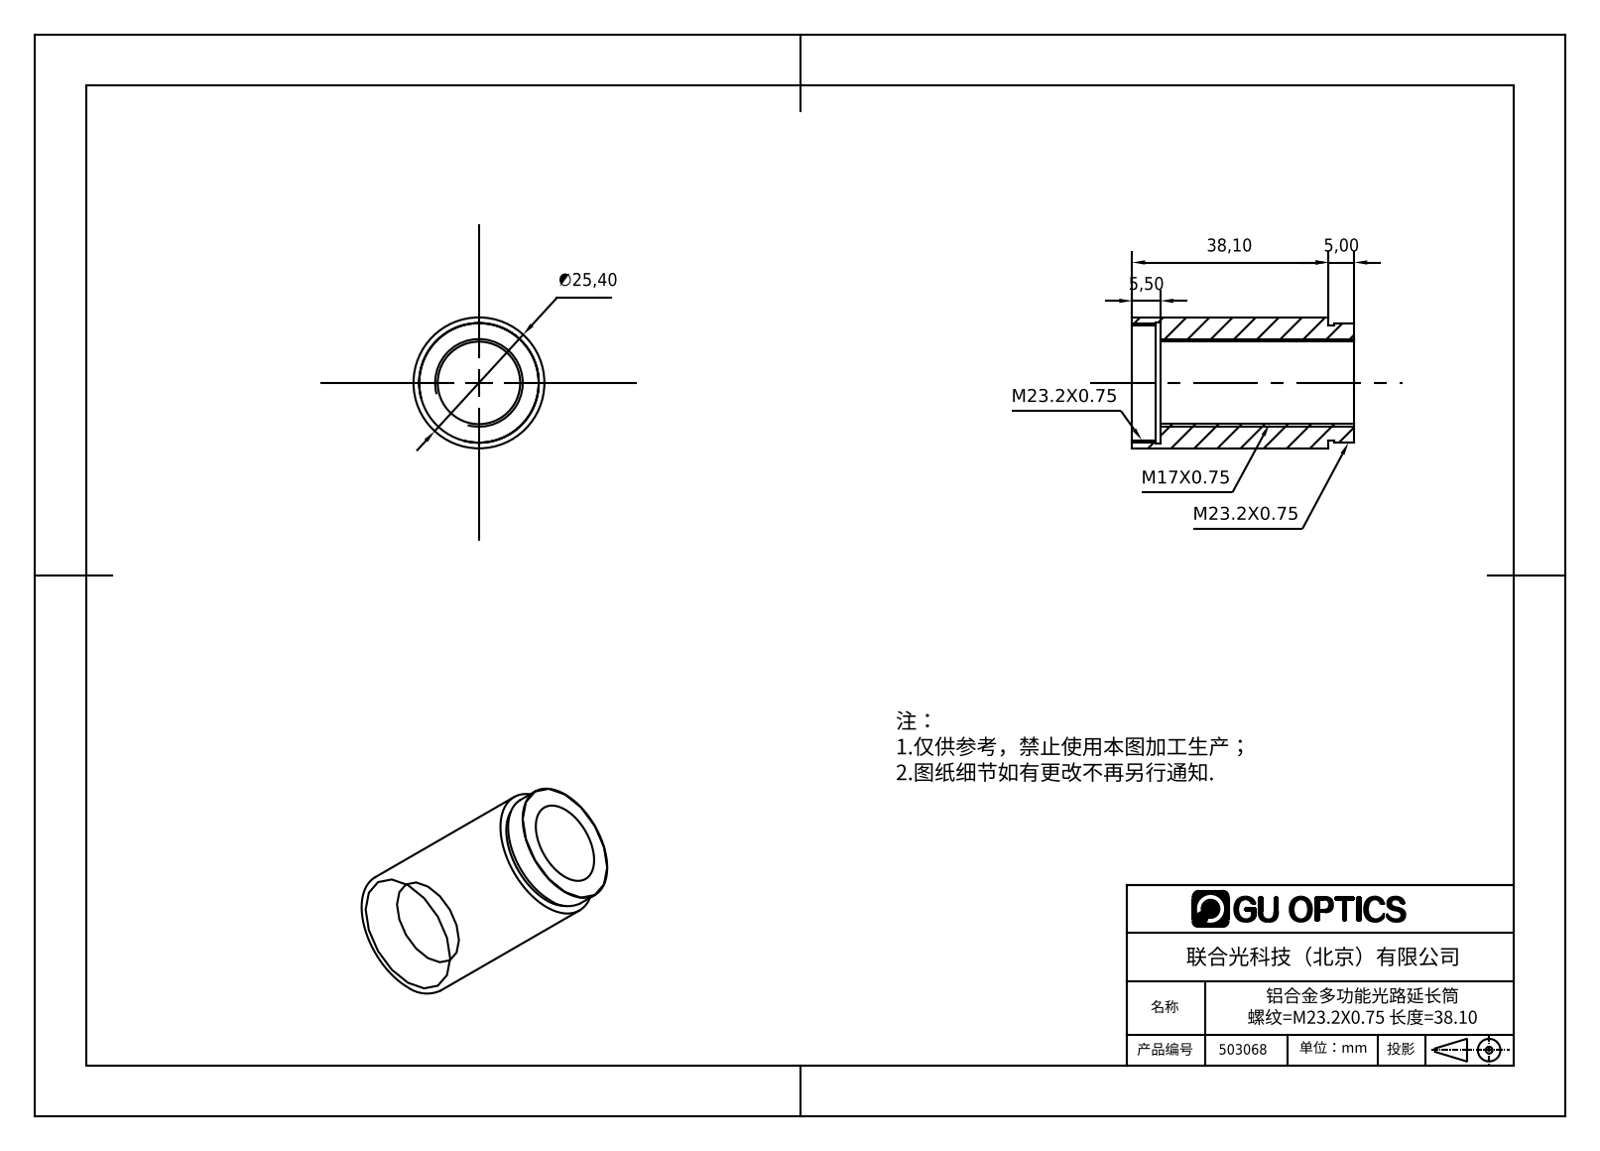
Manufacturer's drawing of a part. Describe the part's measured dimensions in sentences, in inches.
The part is named "503068". Its 3-D file was written by "SolidWorks 2016 (AUTOMOTIVE_DESIGN)". It is 1 solid with 18 faces: 6 planar, 12 cylindrical and 0 other. Overall it measures 1.697 by 1 by 1 inches. Its volume is 0.711 cubic inches and its surface area 9.993 square inches. Round holes: 1 of diameter 0.63, 1 of diameter 0.874, 1 of diameter 0.921. Round bosses or shafts: 1 of diameter 1, 1 of diameter 0.913. The main face-to-face distances are 1.48, 1.283, 0.197, 0.217, 1.5, 1.697, 0.039, 1.323, 0.177, 1.52.
